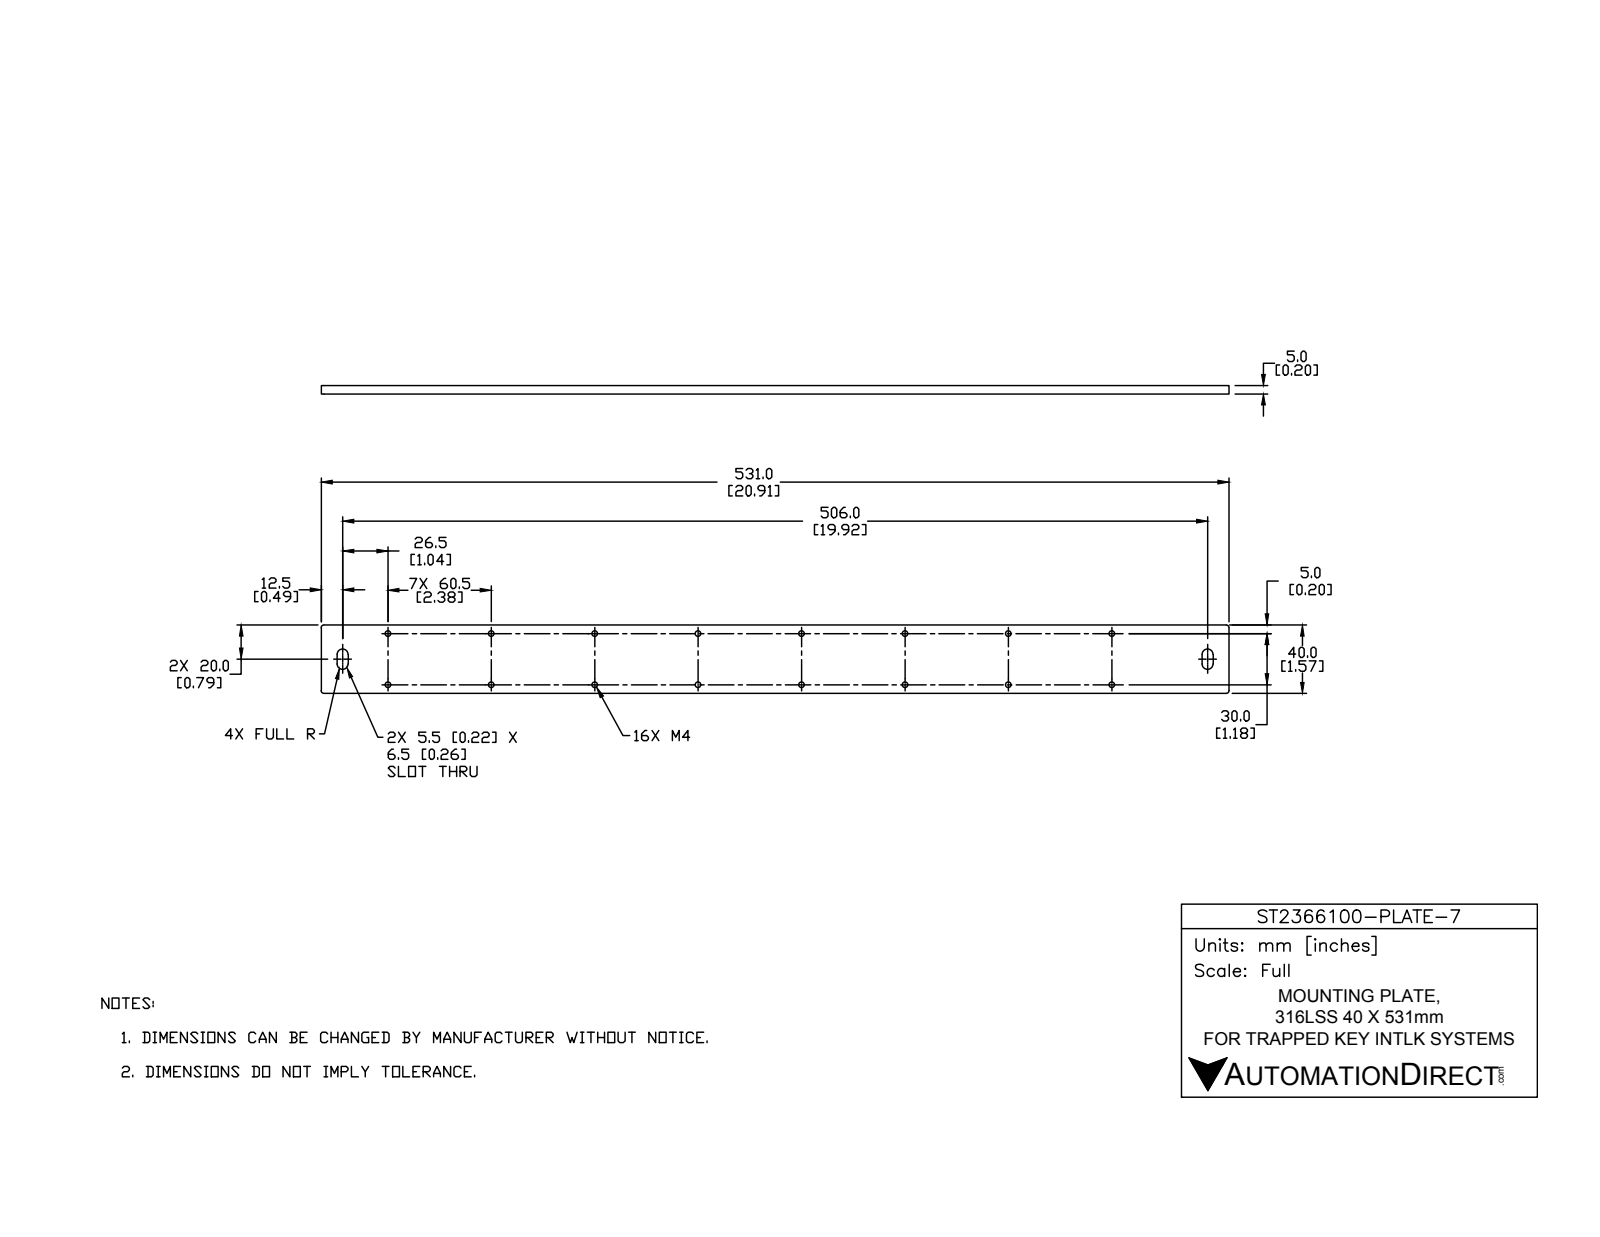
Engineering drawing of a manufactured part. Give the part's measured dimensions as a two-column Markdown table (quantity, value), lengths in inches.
| quantity | value |
| --- | --- |
| part name | ST2366100-PLATE-7 |
| STEP written by | SolidWorks 2017 (AUTOMOTIVE_DESIGN) |
| units | inches |
| bodies | 1 solid, 66 faces (10 planar, 40 cylindrical, 16 other) |
| overall size | 20.906 × 1.575 × 0.197 |
| volume | 6.39 in³ |
| surface area | 74.8 in² |
| round holes (diameter × count) | 0.128 × 16 |
| partial cylindrical surfaces (radius × count) | 0.008 × 8, 0.02 × 8, 0.079 × 4, 0.128 × 4 |
| main face-to-face distances | 0.197, 1.575, 20.906, 0.364, 0.62, 20.285, 20.541, 0.256, 19.921, 20.177 |
| hole center spacings | 2.362, 2.641, 4.724, 4.87, 7.087, 7.184, 1.181, 9.449 |
